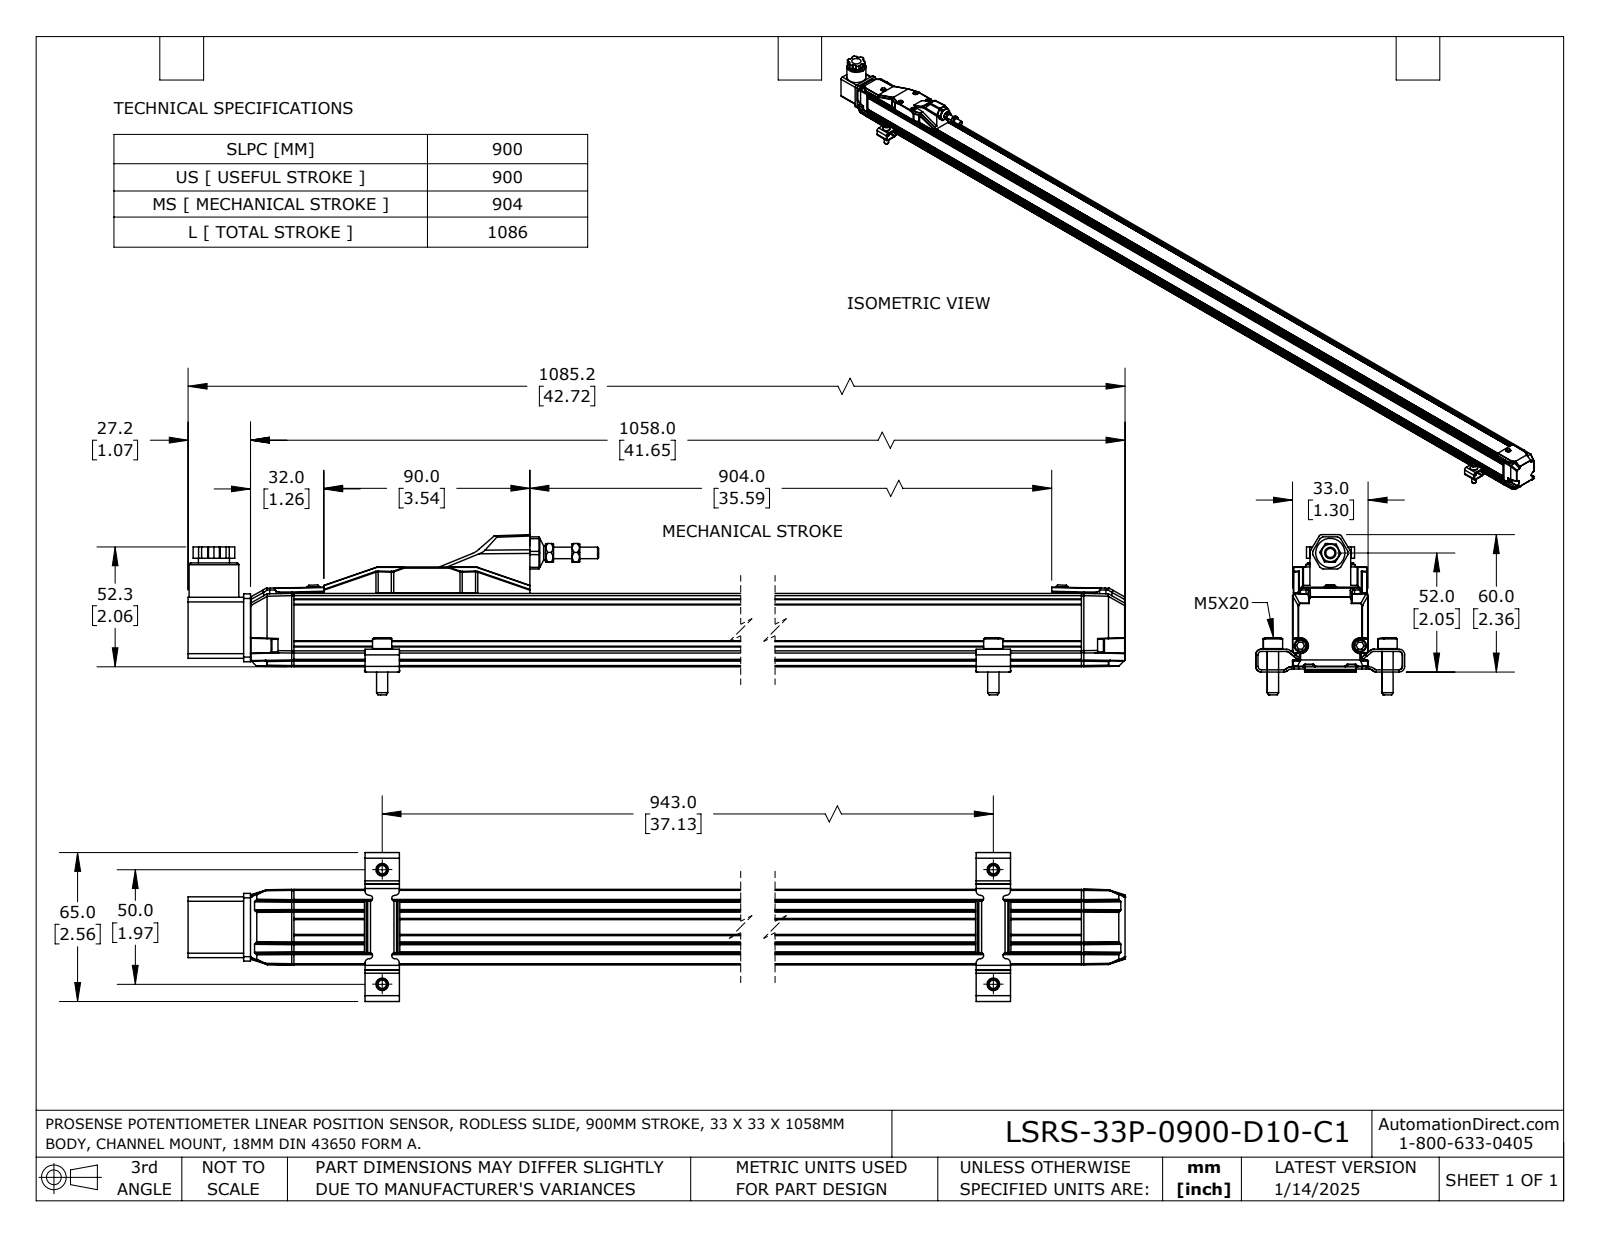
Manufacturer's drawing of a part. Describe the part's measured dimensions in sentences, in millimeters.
The part is named "LSRS-33P-0900-D10-C1". Its 3-D file was written by "SolidWorks 2023 (AUTOMOTIVE_DESIGN)". It is 10 solids with 1310 faces: 821 planar, 357 cylindrical and 132 other. Overall it measures 1085.2 by 70 by 65 millimeters. Its volume is 1 028 000 cubic millimeters and its surface area 234 600 square millimeters. Round holes: 4 of diameter 4.7, 4 of diameter 5.5, 2 of diameter 2.7, 2 of diameter 3.3, 1 of diameter 4, 1 of diameter 5, 1 of diameter 5.3, 1 of diameter 5.9, 1 of diameter 6, 1 of diameter 7, 1 of diameter 10, 1 of diameter 10.5. Round bosses or shafts: 4 of diameter 8.4, 4 of diameter 4.9, 4 of diameter 4.6, 4 of diameter 2.9, 2 of diameter 5.6, 2 of diameter 5.5, 2 of diameter 3, 2 of diameter 2.5. Partial cylindrical surfaces (rounded edges, fillets, slot ends): 78 of radius 0.5, 62 of radius 0.2, 44 of radius 2, 26 of radius 3, 10 of radius 1, 8 of radius 1.3, 8 of radius 1.5, 8 of radius 4. The main face-to-face distances are 33, 3, 31.6, 29.6, 6, 25.6, 0.9, 0.4, 32.6, 11.3. The hole center spacings are 15.2, 20, 23.7, 31, 32.7, 42.5, 50, 914.2.
